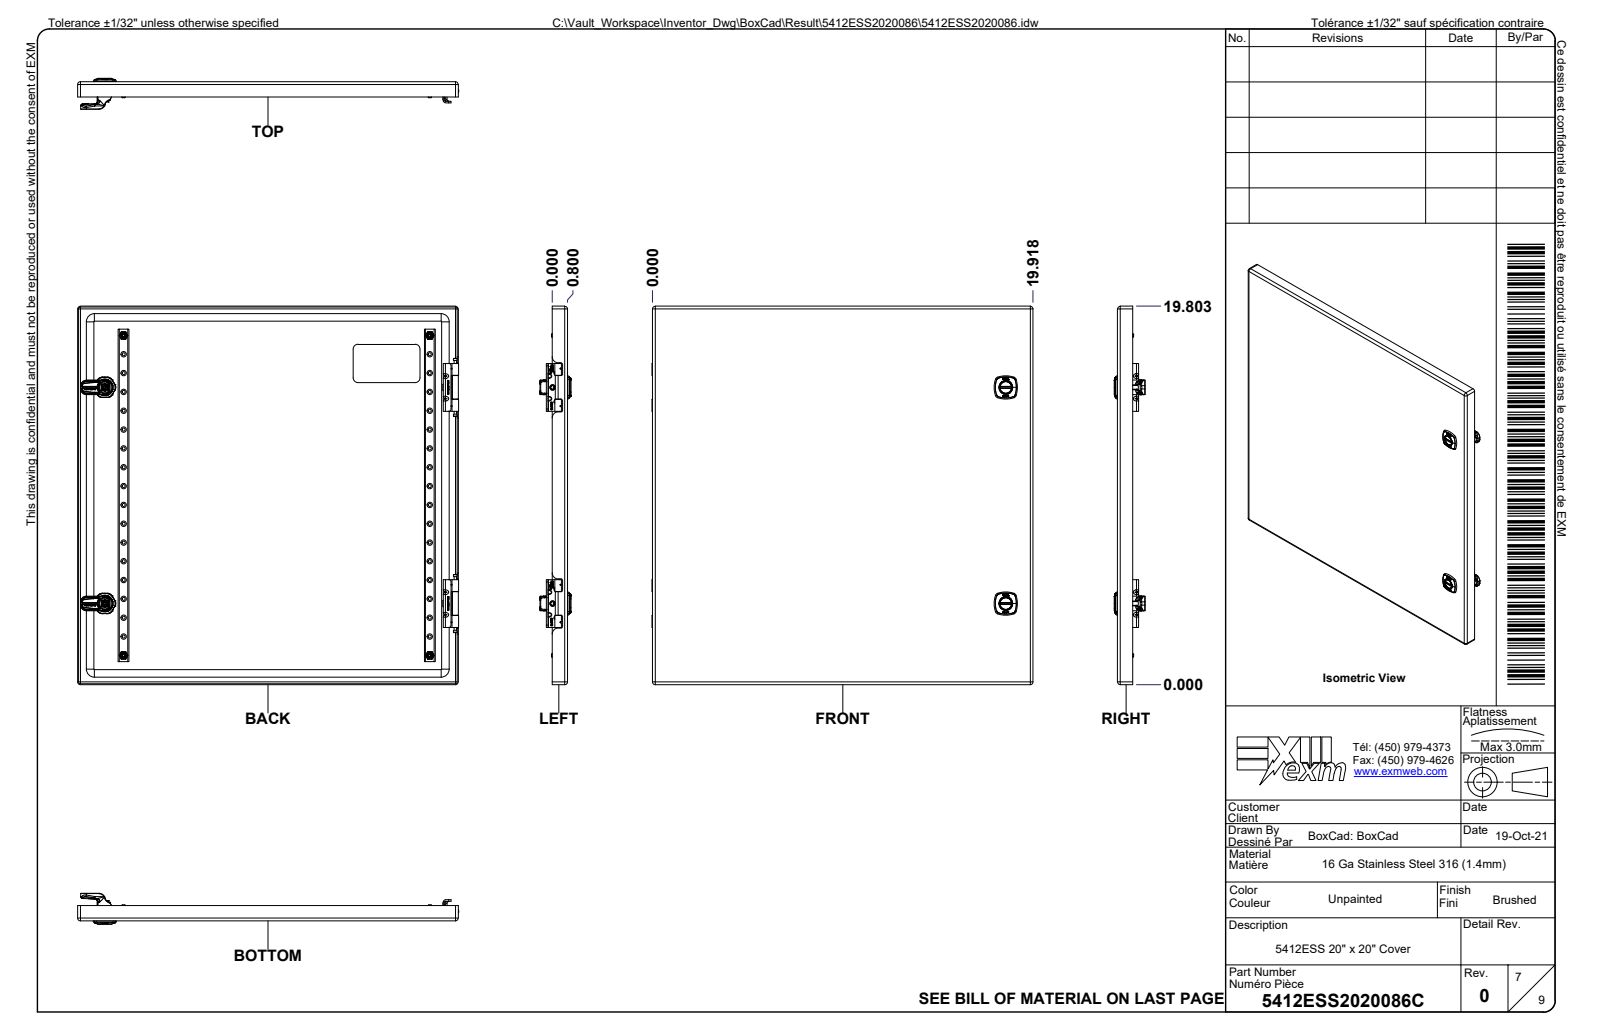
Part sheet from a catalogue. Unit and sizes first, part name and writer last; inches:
Units: inches
Overall size (bounding box): 20 × 20 × 9.306
Round holes (diameter × count): ⌀0.165 ×32, ⌀0.03 ×9, ⌀0.201 ×8, ⌀0.315 ×8, ⌀0.29 ×6, ⌀0.311 ×6, ⌀0.044 ×4, ⌀0.197 ×4, ⌀0.268 ×4, ⌀0.27 ×4, ⌀0.39 ×4, ⌀0.236 ×2
Round bosses / shafts (diameter × count): ⌀0.237 ×32, ⌀0.232 ×9, ⌀0.03 ×9, ⌀0.039 ×8, ⌀0.717 ×4, ⌀0.374 ×4, ⌀0.311 ×4, ⌀0.262 ×4
Partial cylindrical surfaces — rounded edges, fillets, slot ends (radius × count): R0.02 ×106, R0.008 ×68, R0.039 ×66, R0.012 ×34, R0.01 ×28, R0.031 ×26, R0.084 ×24, R0.01 ×16
Main face-to-face distances: 0.053, 9.082, 19.947, 9.029, 9.135, 0.927, 0.874, 8.155, 8.208, 0.105
Hole centre spacings: 0.984, 1.969, 2.953, 3.937, 4.921, 5.906, 6.89, 7.874
Volume: 130.4 in³ · Surface area: 4 193 in²
Bodies: 64 solids, 9210 faces (2989 planar, 1923 cylindrical, 4298 other)
Part name (STEP PRODUCT): 5412ESS2020086; 5412ESS2020086B; 5412ESS2020086B-P; STK-Q-16020 (+8 more)
STEP written by: Autodesk Inventor 2024 (AUTOMOTIVE_DESIGN)
